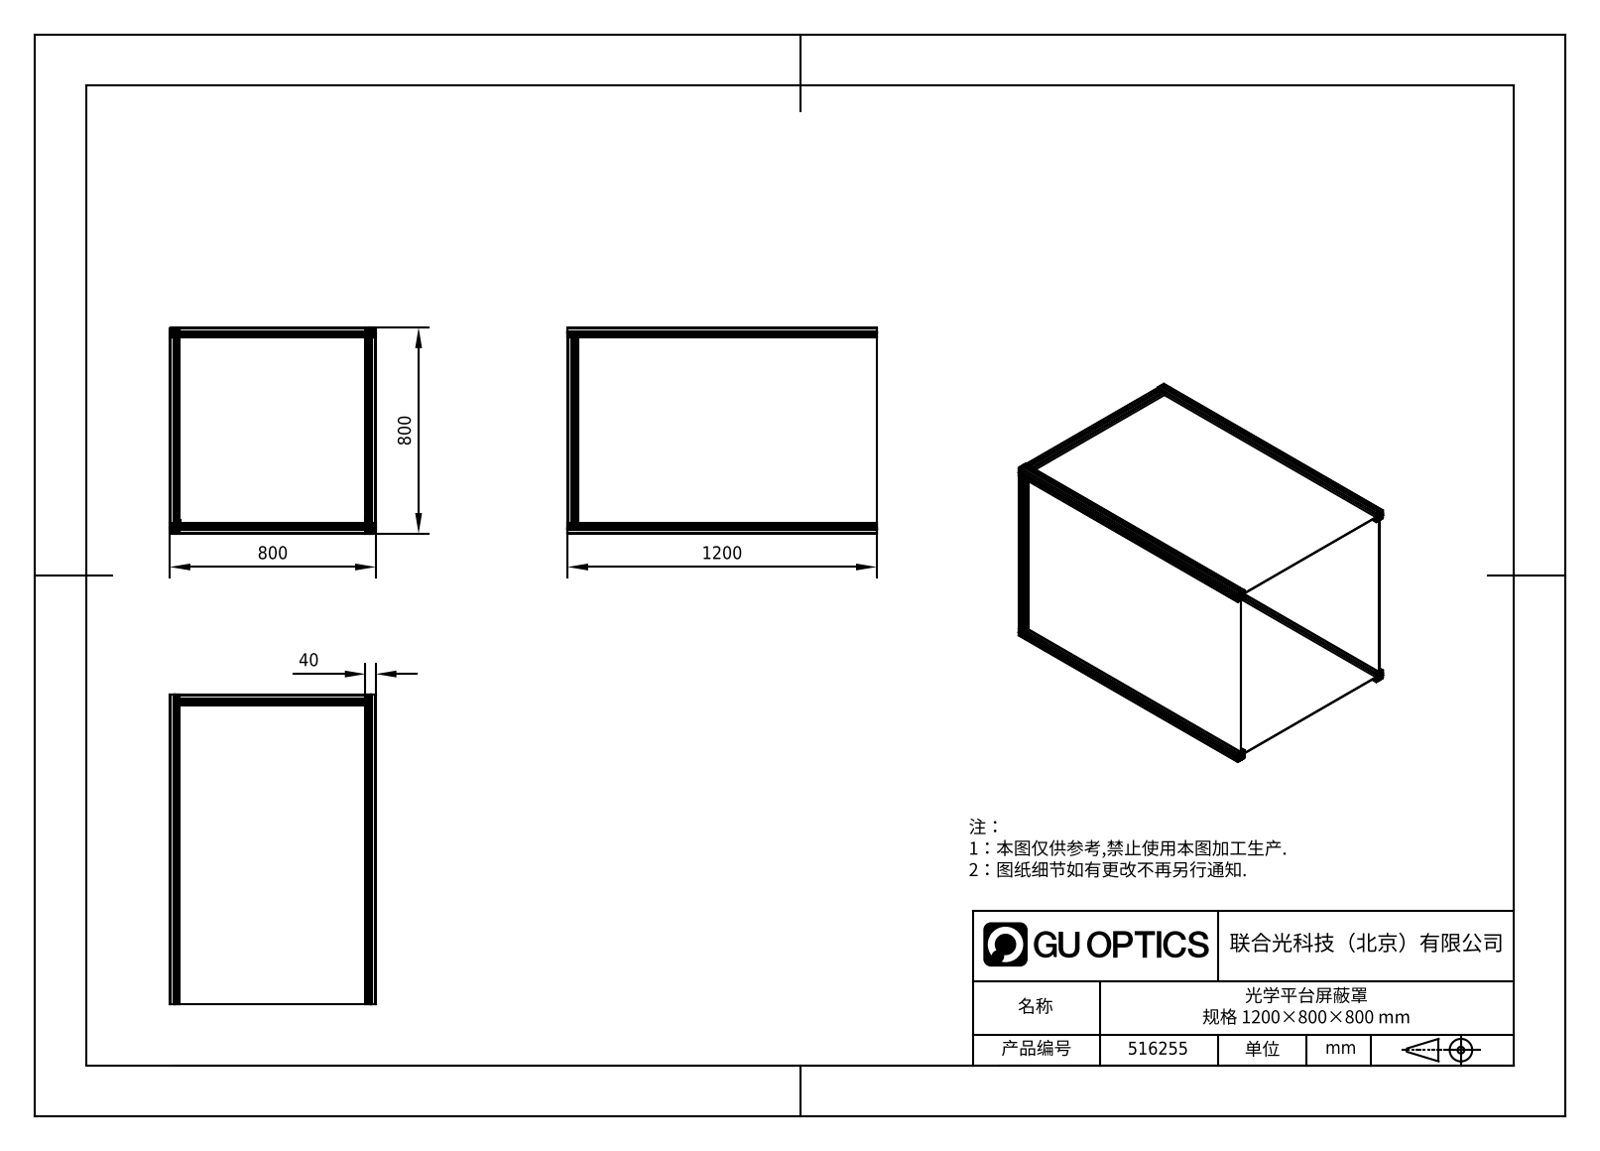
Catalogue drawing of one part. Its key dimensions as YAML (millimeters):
part_name: "光学平台屏蔽罩边框_720; 光学平台屏蔽罩面板_732_1172; 光学平台屏蔽罩面板_744_744; 光学平台屏蔽罩边框_1200 (+2 more)"
step_written_by: "SolidWorks 2020 (CONFIG_CONTROL_DESIGN)"
units: millimeters
bodies: {solids: 13, faces: 1230, planar: 950, cylindrical: 280, other: 0}
overall_size: [1200, 800, 800]
volume: 12630000
surface_area: 11850000
partial_cylinders:
  - {radius: 0.5, count: 64}
  - {radius: 1, count: 64}
  - {radius: 0.75, count: 32}
  - {radius: 2.5, count: 32}
  - {radius: 4.5, count: 32}
  - {radius: 3.4, count: 8}
face_to_face_distances: [760, 2, 762, 758, 19, 8.2, 21, 31.8, 12.4, 1.5]
